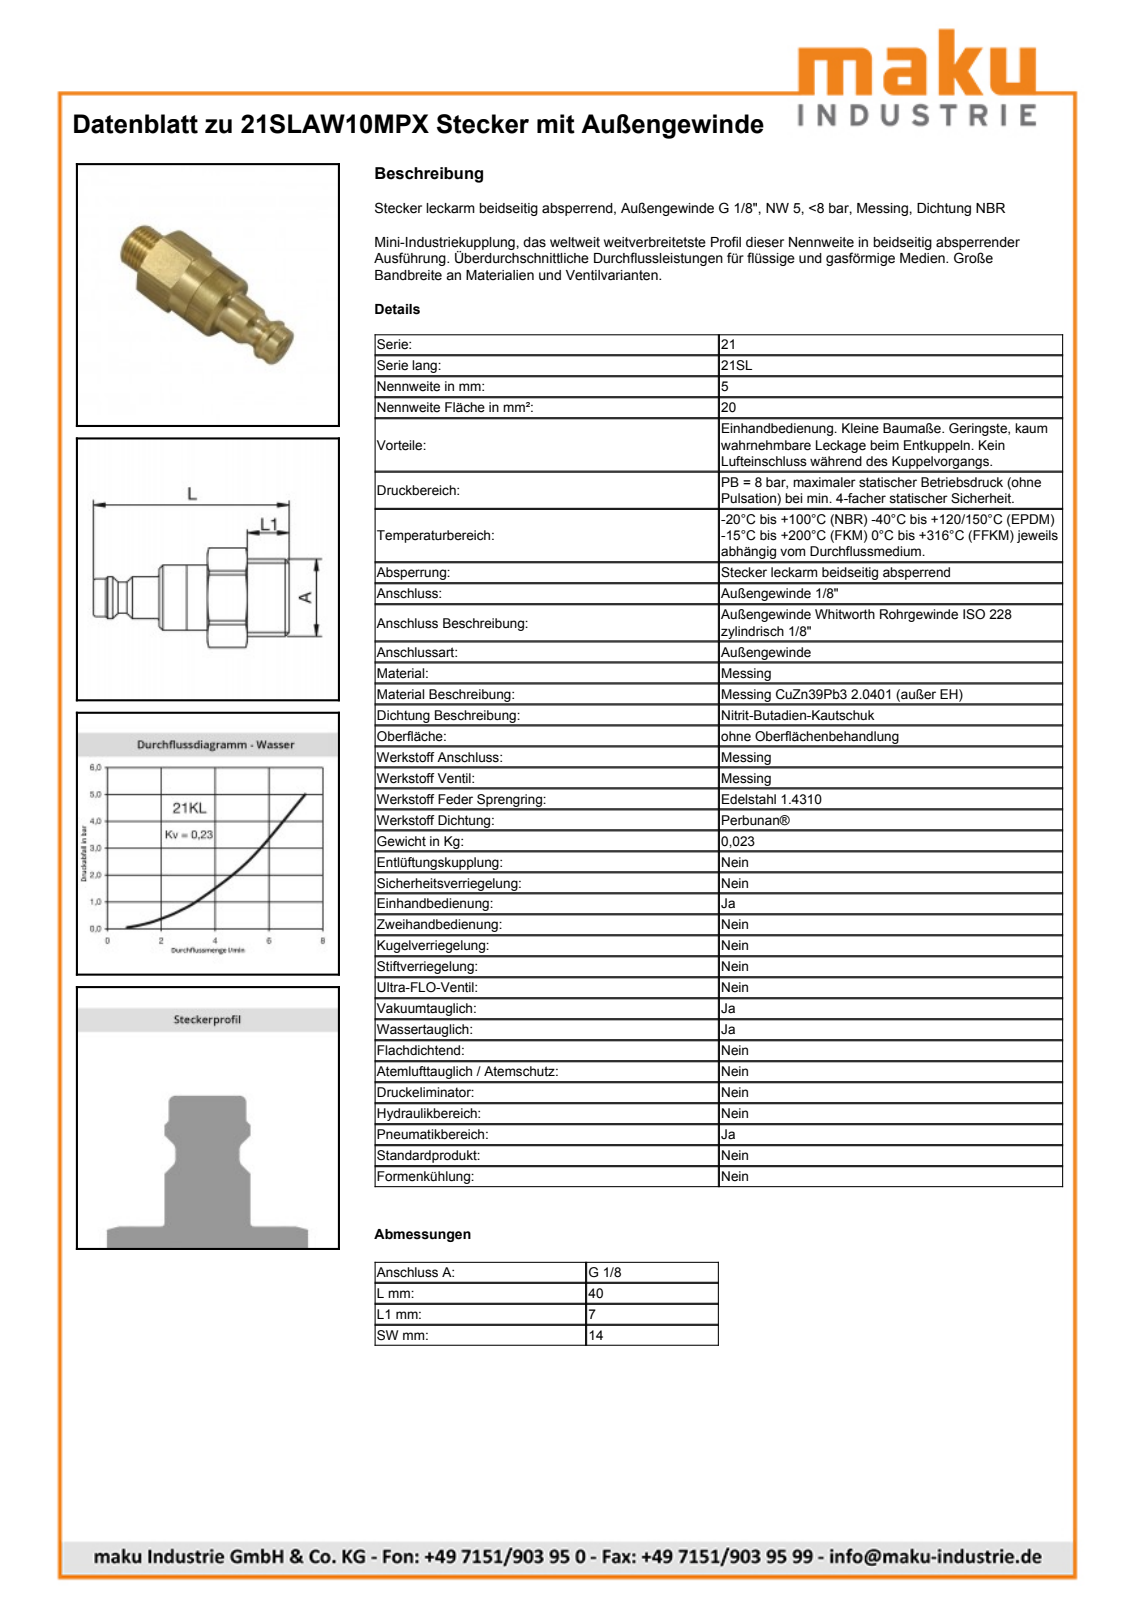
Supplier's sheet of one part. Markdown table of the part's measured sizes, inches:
| quantity | value |
| --- | --- |
| part name | D106293 |
| STEP written by | Autodesk Inventor 2013 (AUTOMOTIVE_DESIGN) |
| units | inches |
| bodies | 1 solid, 52 faces (11 planar, 16 cylindrical, 25 other) |
| overall size | 1.575 × 0.619 × 0.588 |
| volume | 0.261 in³ |
| surface area | 3.36 in² |
| round holes (diameter × count) | 0.472 × 1 |
| round bosses / shafts (diameter × count) | 0.551 × 1, 0.472 × 1, 0.442 × 1, 0.383 × 1, 0.354 × 1, 0.319 × 1, 0.262 × 1 |
| partial cylindrical surfaces (radius × count) | 0.311 × 1 |
| main face-to-face distances | 0.551, 0.276, 0.744, 1.02, 0.555, 1.299, 1.575, 0.945, 0.39, 0.354 |
